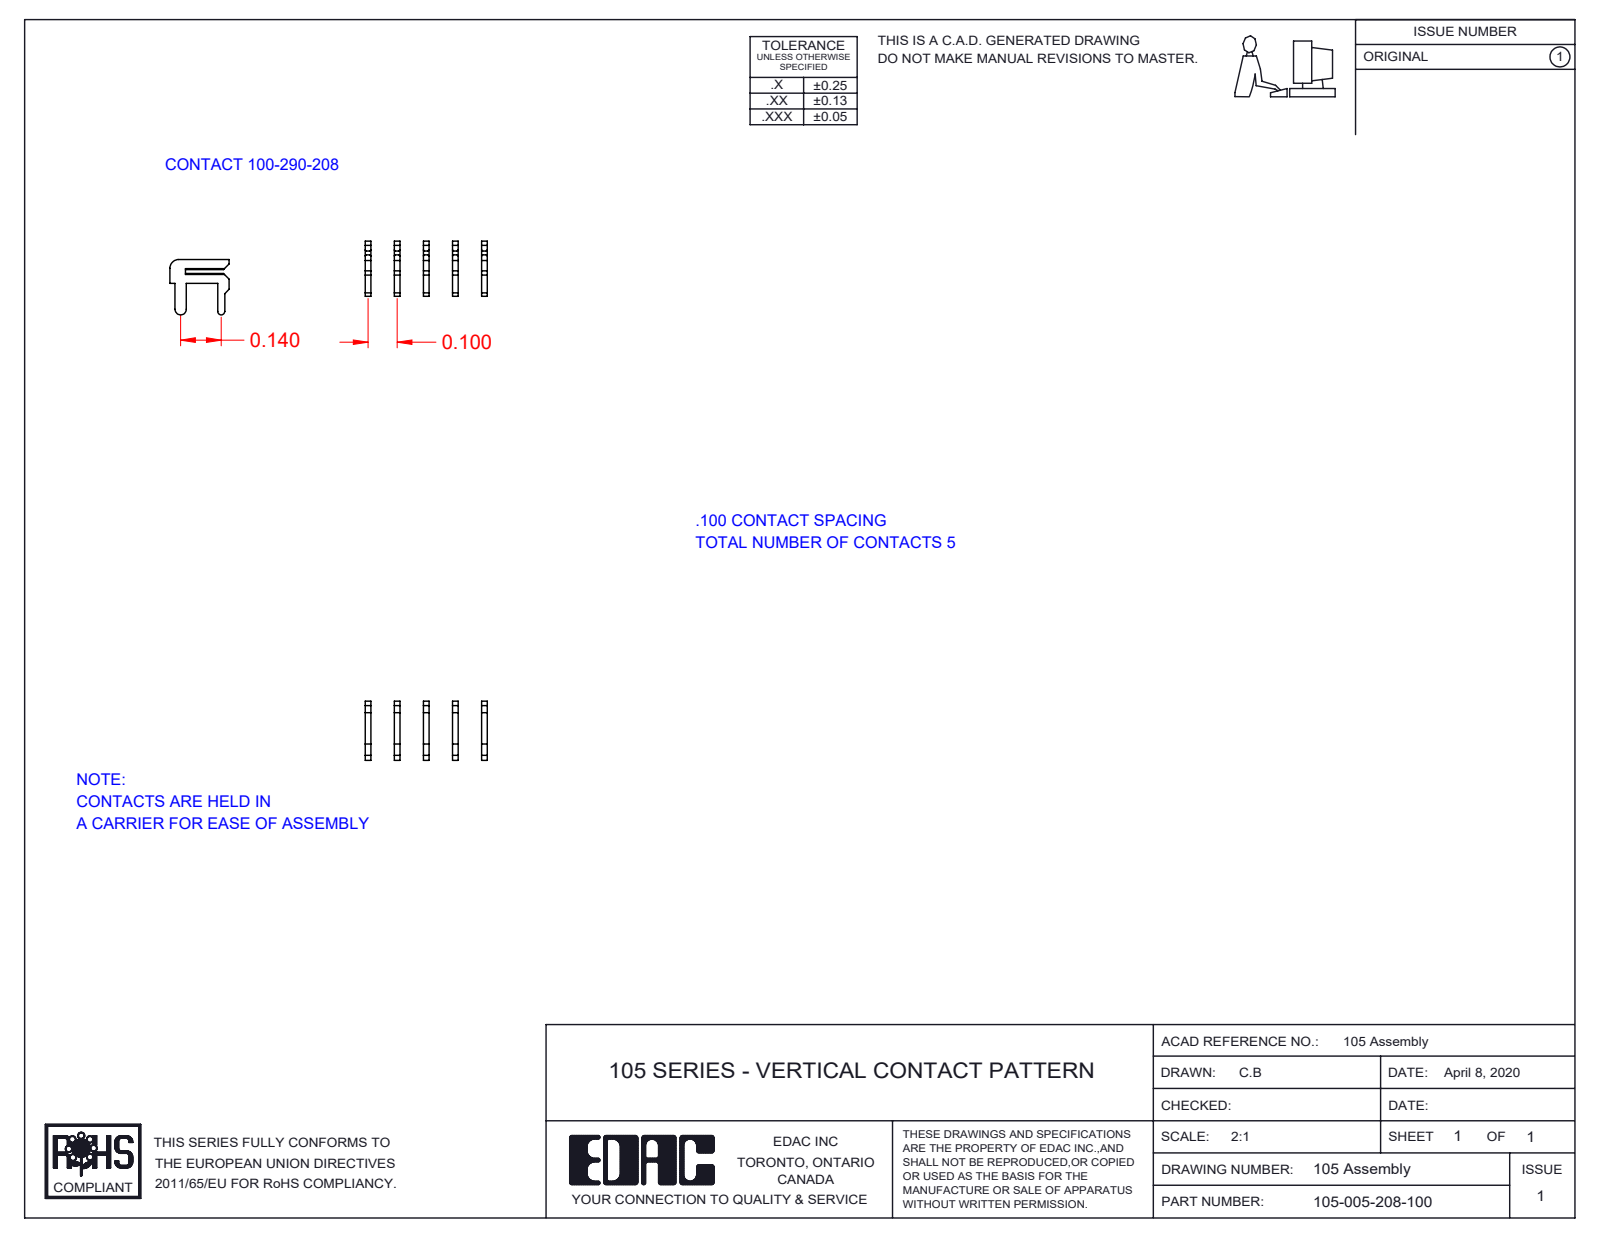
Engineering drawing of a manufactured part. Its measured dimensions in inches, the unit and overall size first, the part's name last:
Units: inches
Overall size (bounding box): 0.42 × 0.204 × 0.19
Partial cylindrical surfaces — rounded edges, fillets, slot ends (radius × count): R0.012 ×1, R0.019 ×1, R0.03 ×1
Main face-to-face distances: 0.1, 0.2, 0.02, 0.3, 0.12, 0.08, 0.22, 0.18, 0.4, 0.32
Volume: 0.002 in³ · Surface area: 0.329 in²
Bodies: 5 solids, 125 faces (110 planar, 15 cylindrical, 0 other)
Part name (STEP PRODUCT): 100-290-001_100-290-208; 105-005-208-100
STEP written by: SolidWorks 2016 (CONFIG_CONTROL_DESIGN)
